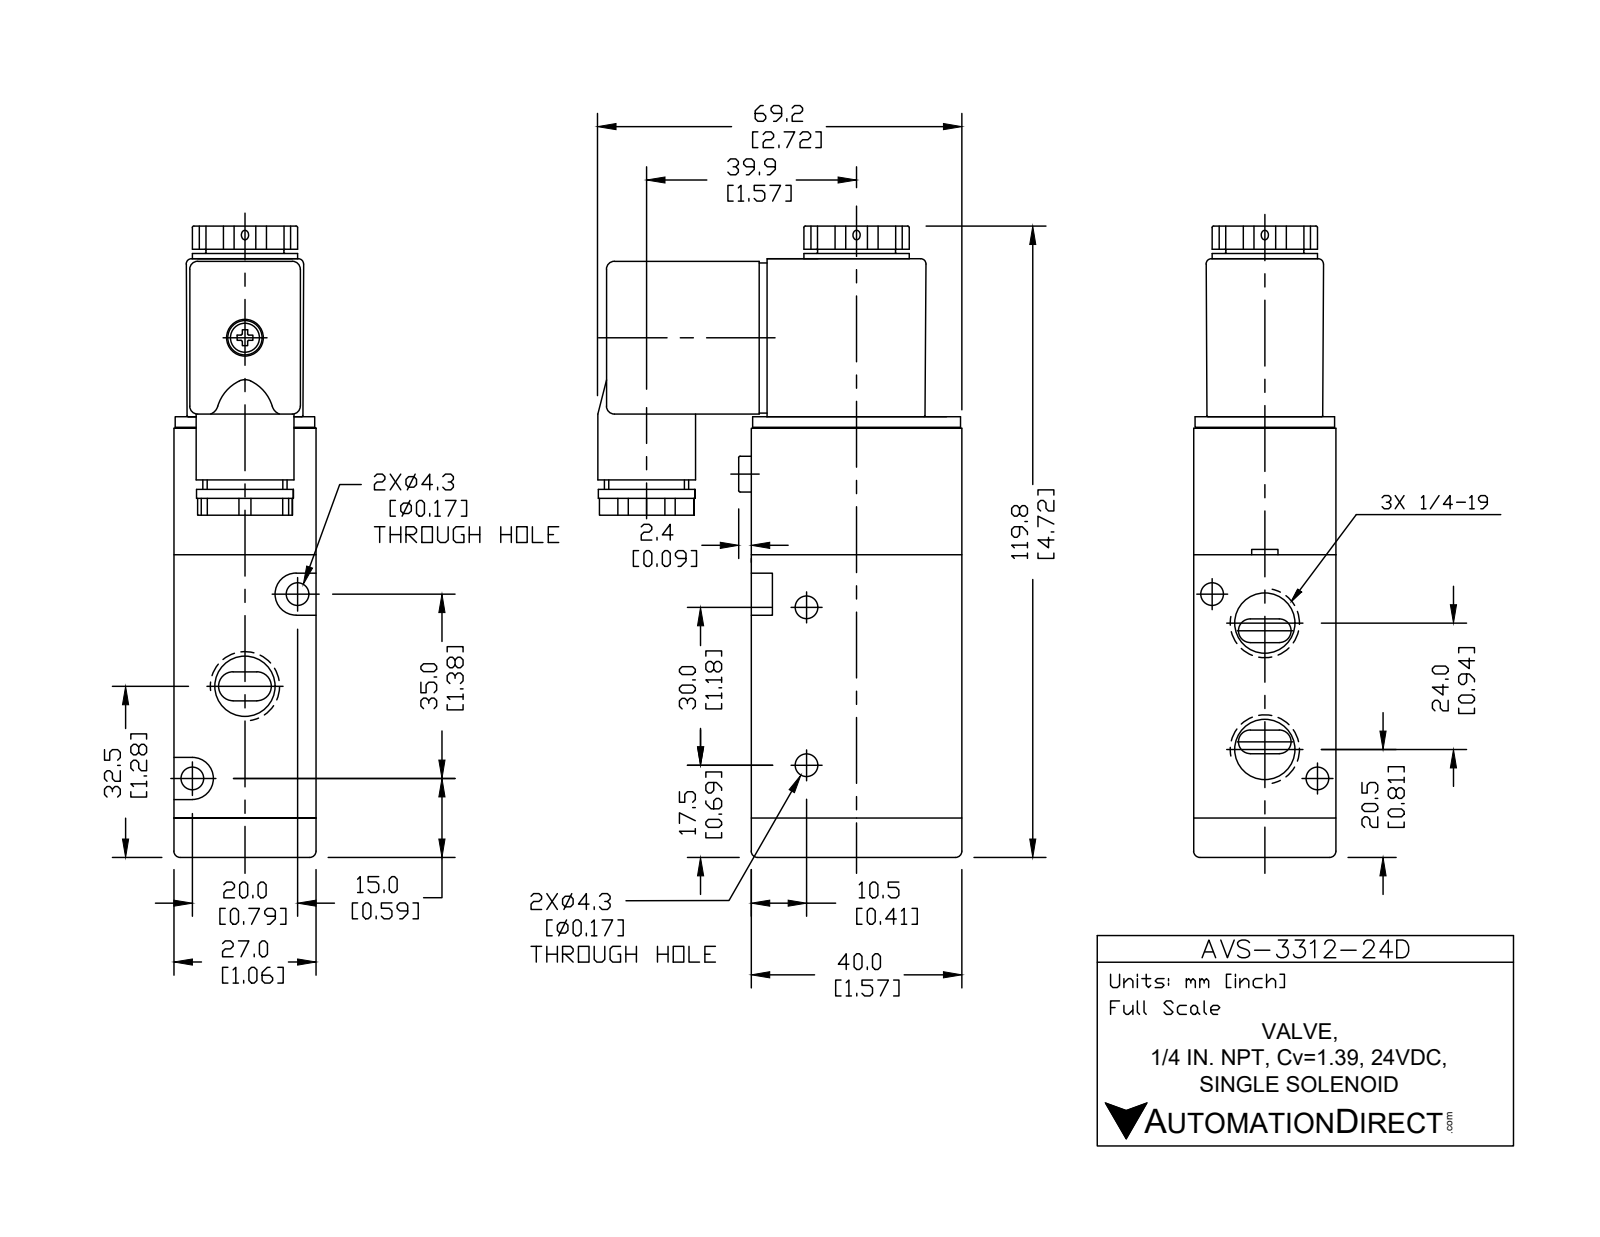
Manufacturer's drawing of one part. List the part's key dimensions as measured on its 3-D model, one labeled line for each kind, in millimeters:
Part name (STEP PRODUCT): AVS-3312-24D
STEP written by: SolidWorks 2015 (CONFIG_CONTROL_DESIGN)
Units: millimetres
Bodies: 4 solids, 156 faces (81 planar, 53 cylindrical, 22 other)
Overall size (bounding box): 119.9 × 69.1 × 27
Volume: 127 198 mm³ · Surface area: 29 011 mm²
Round holes (diameter × count): ⌀4.3 ×4, ⌀11.13 ×3, ⌀9.3 ×1
Round bosses / shafts (diameter × count): ⌀20 ×1, ⌀18.6 ×1, ⌀18.4 ×1, ⌀16 ×1, ⌀14.8 ×1, ⌀6.8 ×1
Partial cylindrical surfaces — rounded edges, fillets, slot ends (radius × count): R0.5 ×11, R1 ×10, R4 ×2
Main face-to-face distances: 50, 27, 3, 24, 7.5, 57.5, 40, 21, 2.26, 2.27
Hole centre spacings: 11.41, 12.09, 31.15, 19.46, 20.94, 24, 30, 40.31
